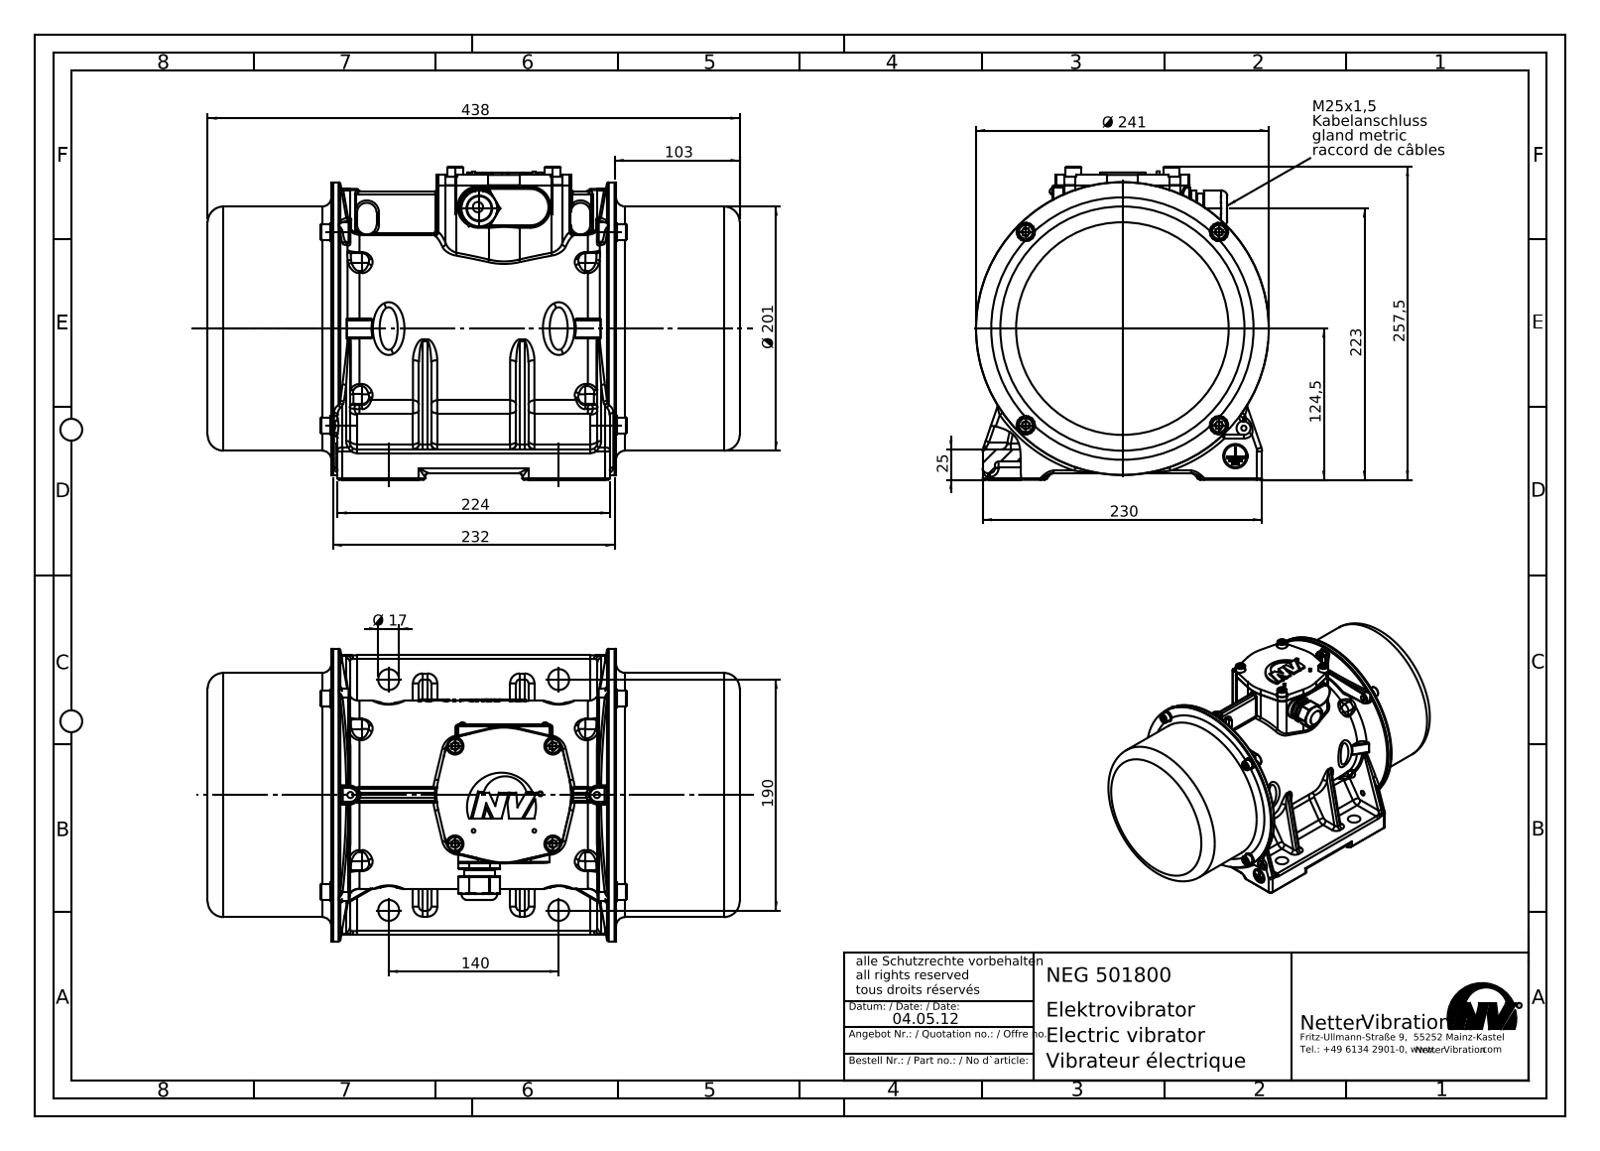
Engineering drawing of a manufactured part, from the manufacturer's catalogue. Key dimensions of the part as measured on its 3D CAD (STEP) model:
Part name (STEP PRODUCT): NEG 501800
STEP written by: SolidWorks 2015 (AUTOMOTIVE_DESIGN)
Units: millimetres
Bodies: 12 solids, 3000 faces (1316 planar, 237 cylindrical, 1447 other)
Overall size (bounding box): 438 × 257.54 × 241
Volume: 3 981 000 mm³ · Surface area: 1 004 000 mm²
Round holes (diameter × count): ⌀3.4 ×4, ⌀3.5 ×4, ⌀6.8 ×4, ⌀8.4 ×4, ⌀9 ×4, ⌀17.2 ×4, ⌀20 ×1, ⌀23.5 ×1, ⌀120 ×1, ⌀198.6 ×1
Round bosses / shafts (diameter × count): ⌀13 ×8, ⌀15 ×4, ⌀8 ×4, ⌀3 ×4, ⌀241 ×1, ⌀201 ×1, ⌀195 ×1, ⌀25 ×1
Partial cylindrical surfaces — rounded edges, fillets, slot ends (radius × count): R0.5 ×30, R2.5 ×8, R1 ×4, R4 ×4
Main face-to-face distances: 101.8, 1.2, 335, 333.8, 103, 436.8, 232, 10, 435.6, 438
Hole centre spacings: 112.5, 159.1, 56, 68, 88.09, 140, 190, 225
